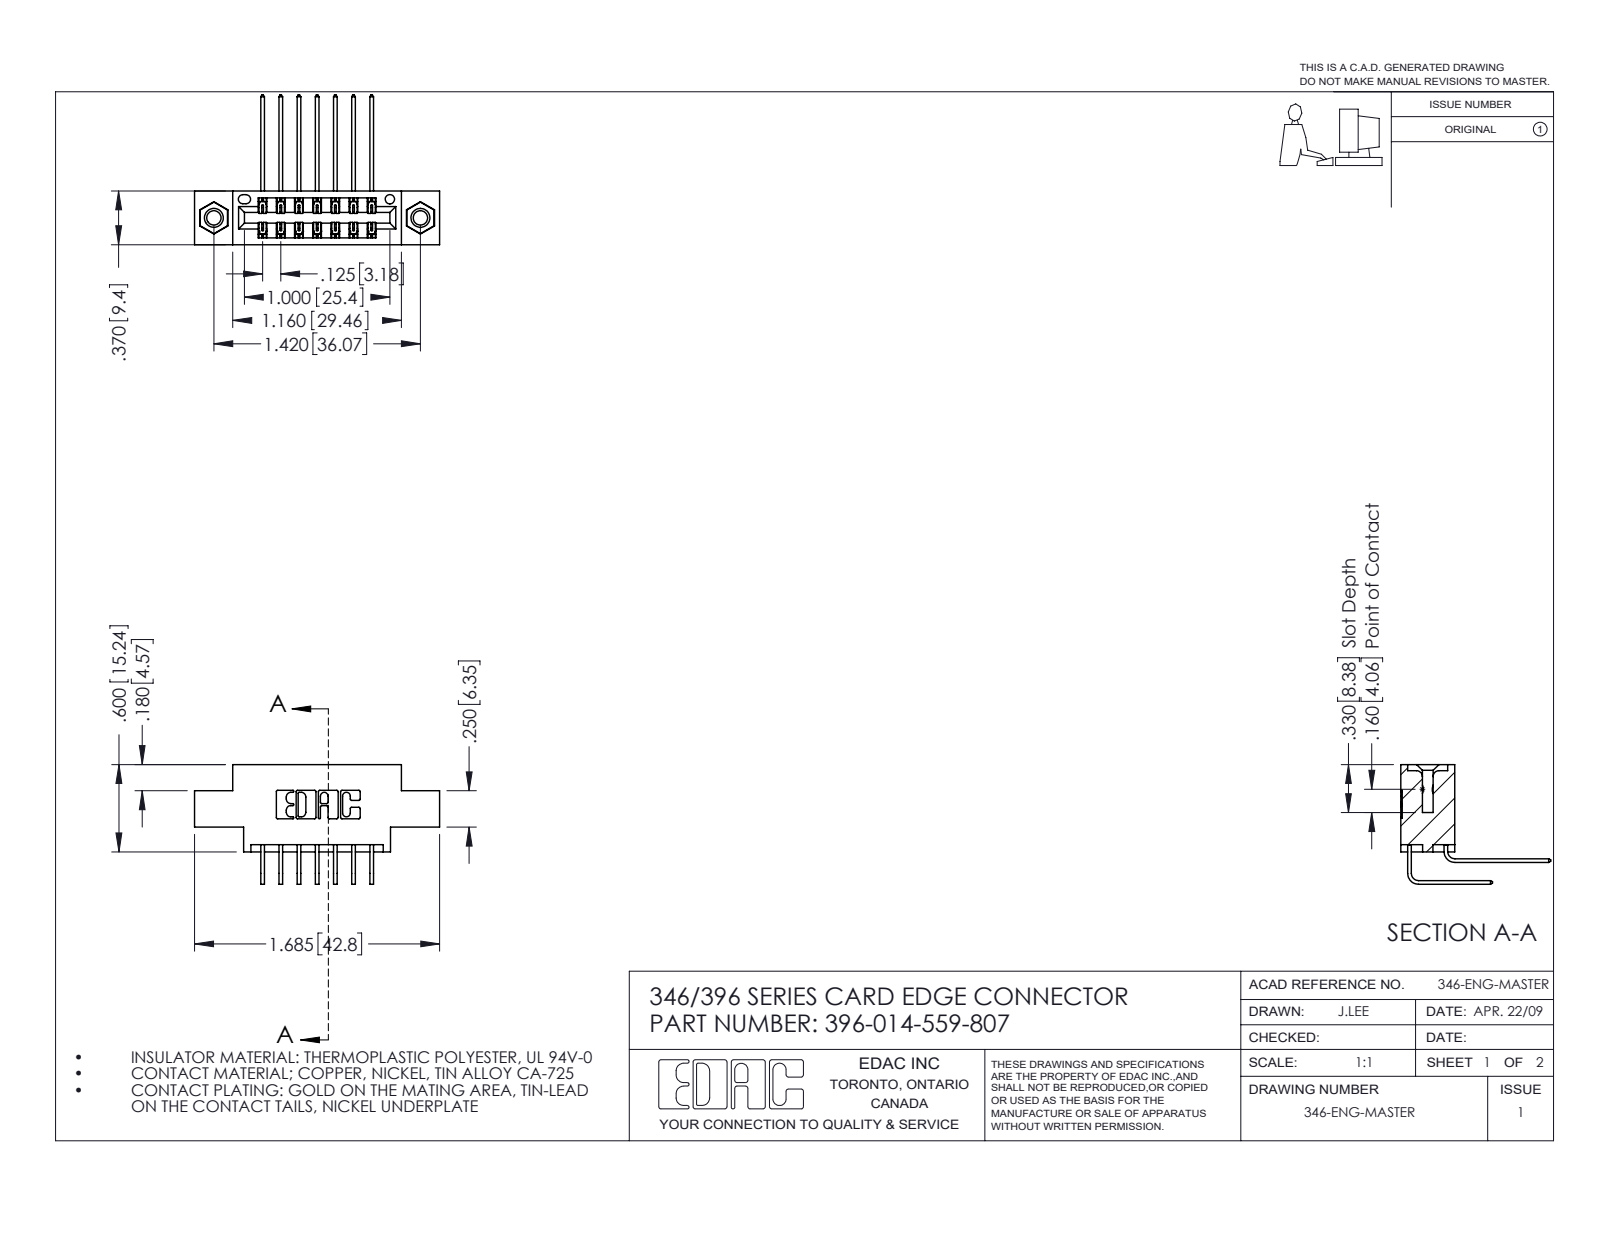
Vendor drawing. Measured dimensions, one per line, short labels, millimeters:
name: 346 Part_0.170 Offset - 0.156 Dia-TI; 345-292-001_558 559 Tail - 1; 396-014-559-807; 345-250-001_345-250-005-103 (+1 more)
written by: SolidWorks 2016 (CONFIG_CONTROL_DESIGN)
unit: mm
bodies: 17 solids, 942 faces (630 planar, 296 cylindrical, 16 other)
size: 42.8 × 26.2 × 20.9
volume: 3 820 mm³; area: 5 294 mm²
holes: 2× ⌀2.5, 2× ⌀3.2, 2× ⌀4, 1× ⌀1.6
bosses: 2× ⌀3.9
rounds: 22× R0.3, 21× R0.2, 6× R0.2, 6× R0.8, 3× R0.7, 2× R0.4, 2× R0.6, 2× R0.6
face distances: 6.4, 1.2, 9.4, 8.2, 0.6, 1.8, 3.2, 5.6, 3.8, 7.6
hole spacings: 6.2, 30.9, 36.1
